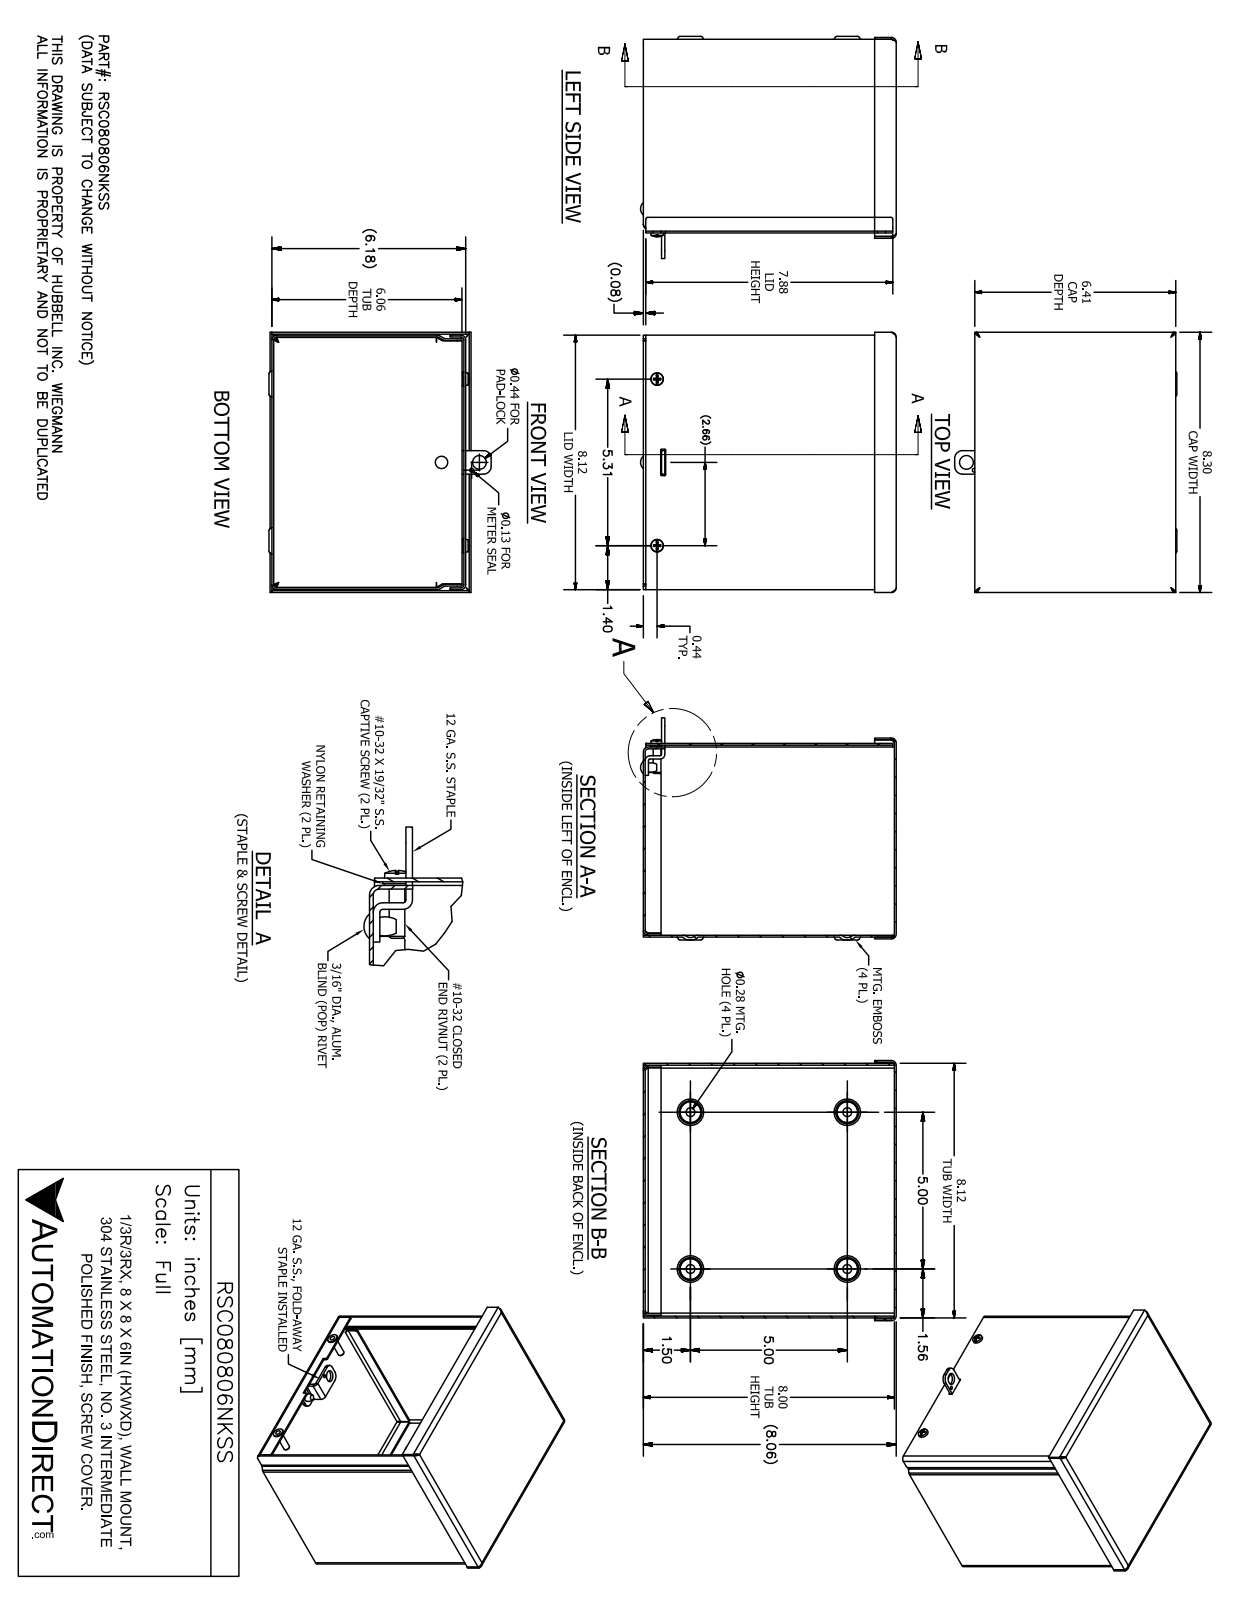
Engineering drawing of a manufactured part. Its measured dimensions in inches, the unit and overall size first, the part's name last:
Units: inches
Overall size (bounding box): 8.299 × 8.149 × 7.084
Round holes (diameter × count): ⌀0.25 ×4, ⌀0.281 ×4, ⌀0.156 ×2, ⌀0.196 ×2, ⌀0.257 ×2, ⌀0.278 ×2, ⌀0.125 ×1, ⌀0.198 ×1, ⌀0.201 ×1, ⌀0.437 ×1
Round bosses / shafts (diameter × count): ⌀0.453 ×2, ⌀0.406 ×2, ⌀0.248 ×2, ⌀0.167 ×2, ⌀0.187 ×1
Partial cylindrical surfaces — rounded edges, fillets, slot ends (radius × count): R0.094 ×16, R0.153 ×16, R0.031 ×6, R0.25 ×4, R0.047 ×2, R0.05 ×2, R0.063 ×2, R0.089 ×2
Main face-to-face distances: 0.059, 8, 8.059, 6.117, 6.176, 6.058, 7.941, 8.118, 0.117, 0.059
Hole centre spacings: 5, 1.074, 1.105, 5.265, 5.271, 5.313, 6.065, 6.096
Volume: 21.54 in³ · Surface area: 739.2 in²
Bodies: 12 solids, 369 faces (191 planar, 93 cylindrical, 85 other)
Part name (STEP PRODUCT): RSC080806NKSS
STEP written by: SolidWorks 2017 (AUTOMOTIVE_DESIGN)
